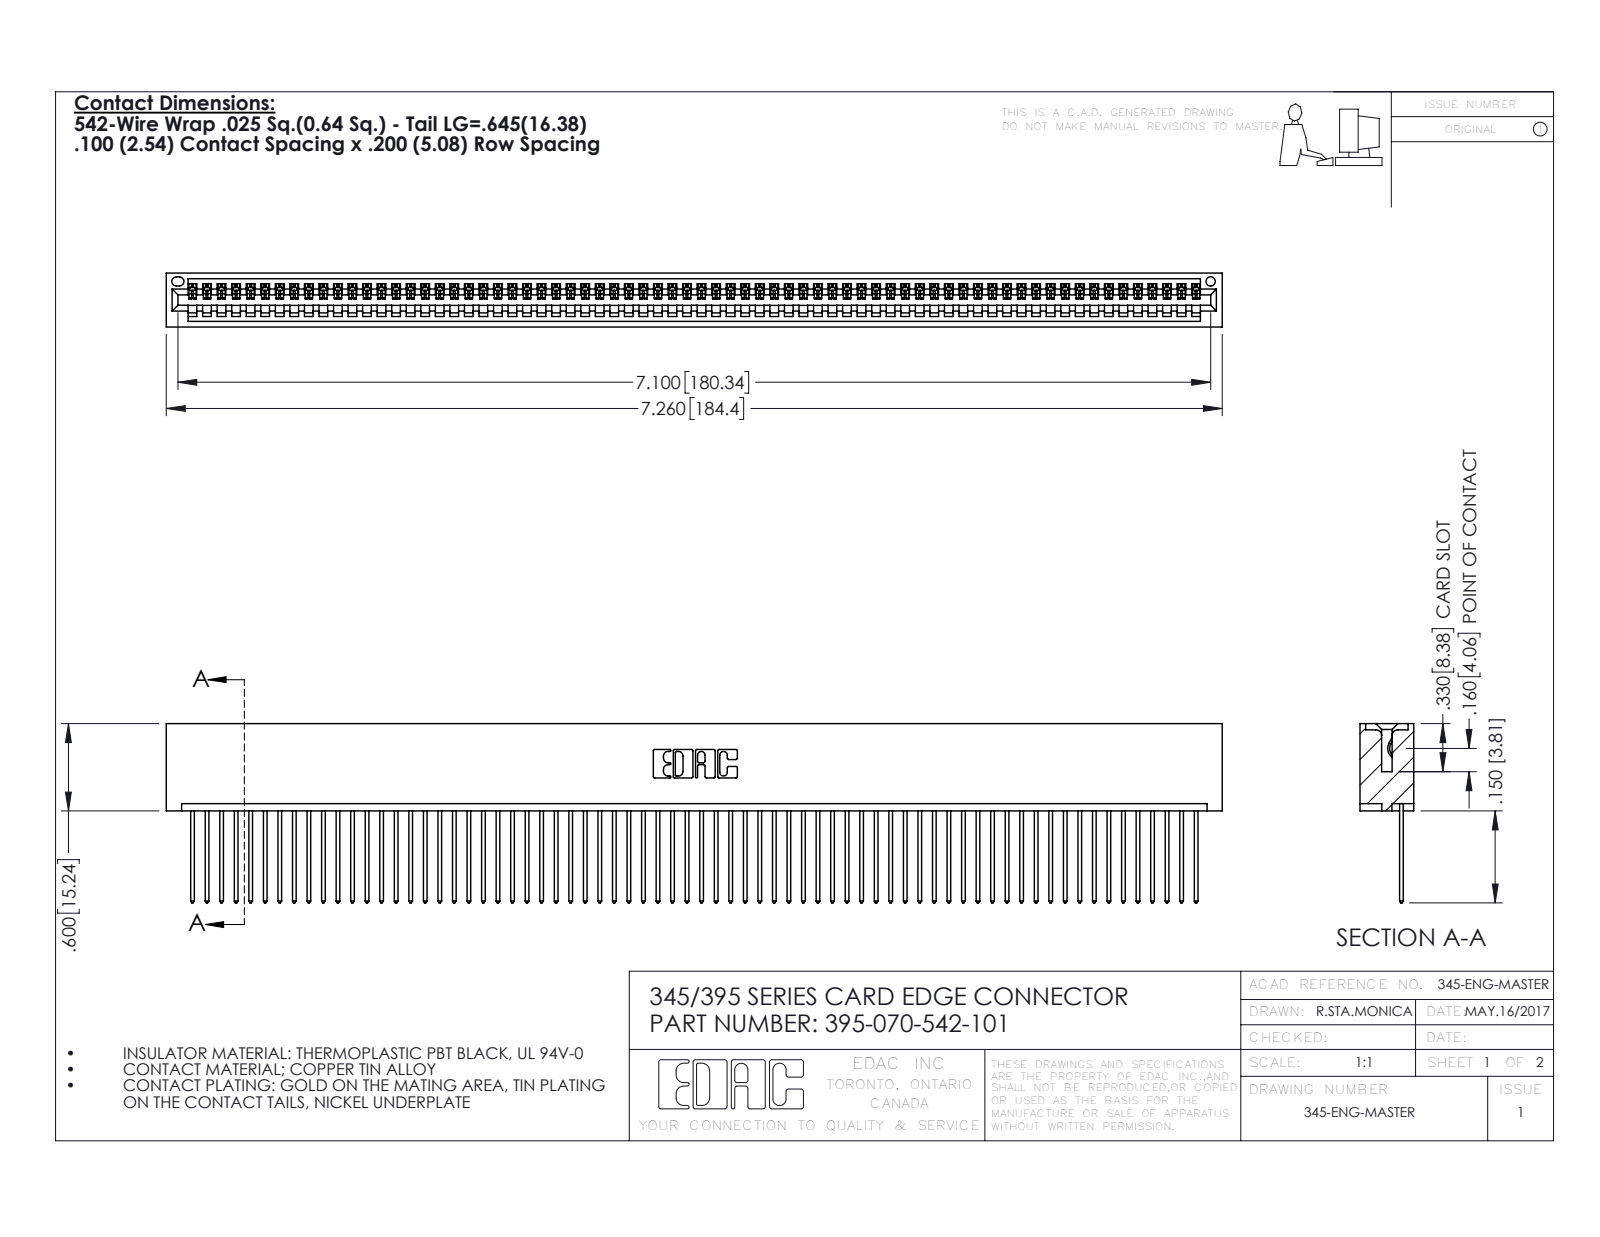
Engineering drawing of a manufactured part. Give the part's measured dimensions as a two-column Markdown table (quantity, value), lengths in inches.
| quantity | value |
| --- | --- |
| part name | 345 Part_No Mounting Lugs; 395-070-542-101; 345-292-001_345-293-142 |
| STEP written by | SolidWorks 2016 (CONFIG_CONTROL_DESIGN) |
| units | inches |
| bodies | 71 solids, 4178 faces (2876 planar, 1302 cylindrical, 0 other) |
| overall size | 7.26 × 1.232 × 0.37 |
| volume | 1.128 in³ |
| surface area | 40.49 in² |
| round holes (diameter × count) | 0.064 × 1 |
| partial cylindrical surfaces (radius × count) | 0.006 × 140, 0.01 × 140, 0.01 × 22, 0.007 × 6, 0.031 × 6, 0.026 × 3, 0.031 × 2, 0.04 × 2 |
| main face-to-face distances | 0.072, 0.298, 0.098, 0.272, 0.025, 0.37, 0.2, 0.225, 0.149, 0.072 |
